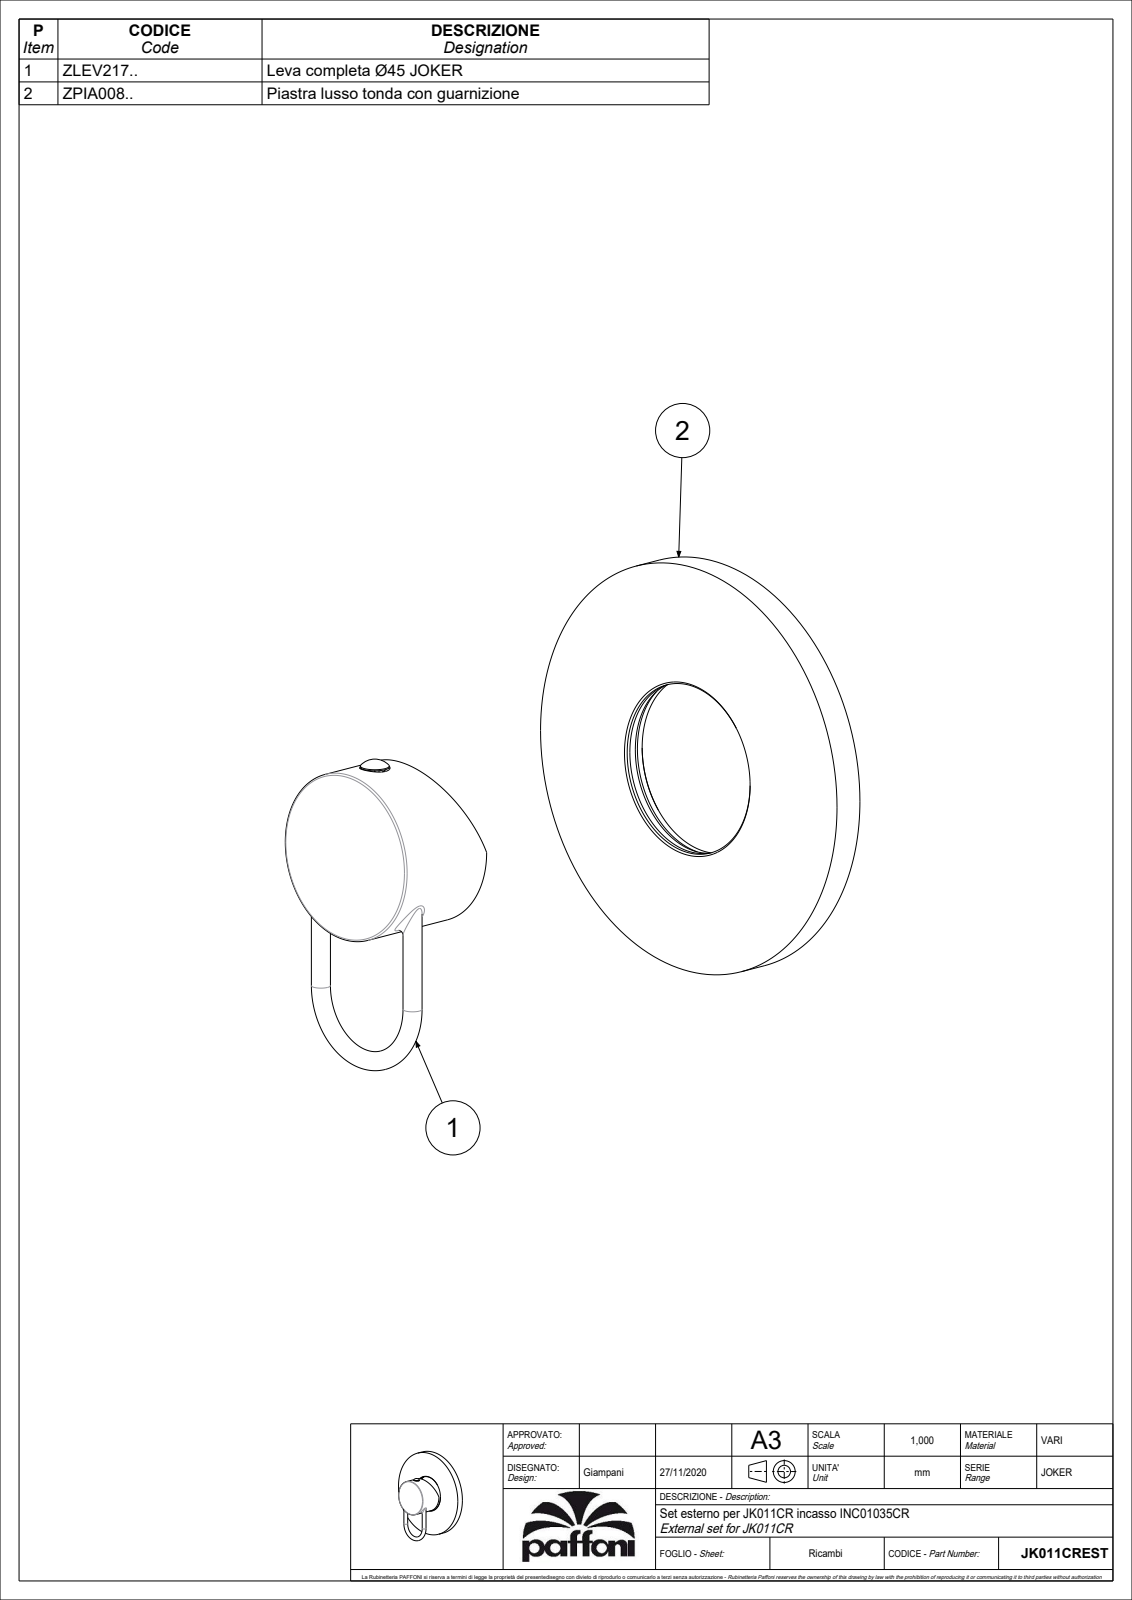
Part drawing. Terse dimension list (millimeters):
name: JK011CREST
written by: CREO PARAMETRIC BY PTC INC, 2020044 (CONFIG_CONTROL_DESIGN)
unit: mm
bodies: 2 solids, 132 faces (45 planar, 48 cylindrical, 39 other)
size: 114 × 110 × 41.39
volume: 38 071 mm³; area: 37 142 mm²
holes: 1× ⌀3, 1× ⌀8, 1× ⌀45.6, 1× ⌀47.6, 1× ⌀51.5, 1× ⌀105
bosses: 3× ⌀5, 1× ⌀110, 1× ⌀54.6, 1× ⌀45, 1× ⌀7.6, 1× ⌀5.5
rounds: 2× R1.55
face distances: 30, 7, 37, 1.5, 5.5, 35.5, 7.56, 6.06, 0.56, 29.44
